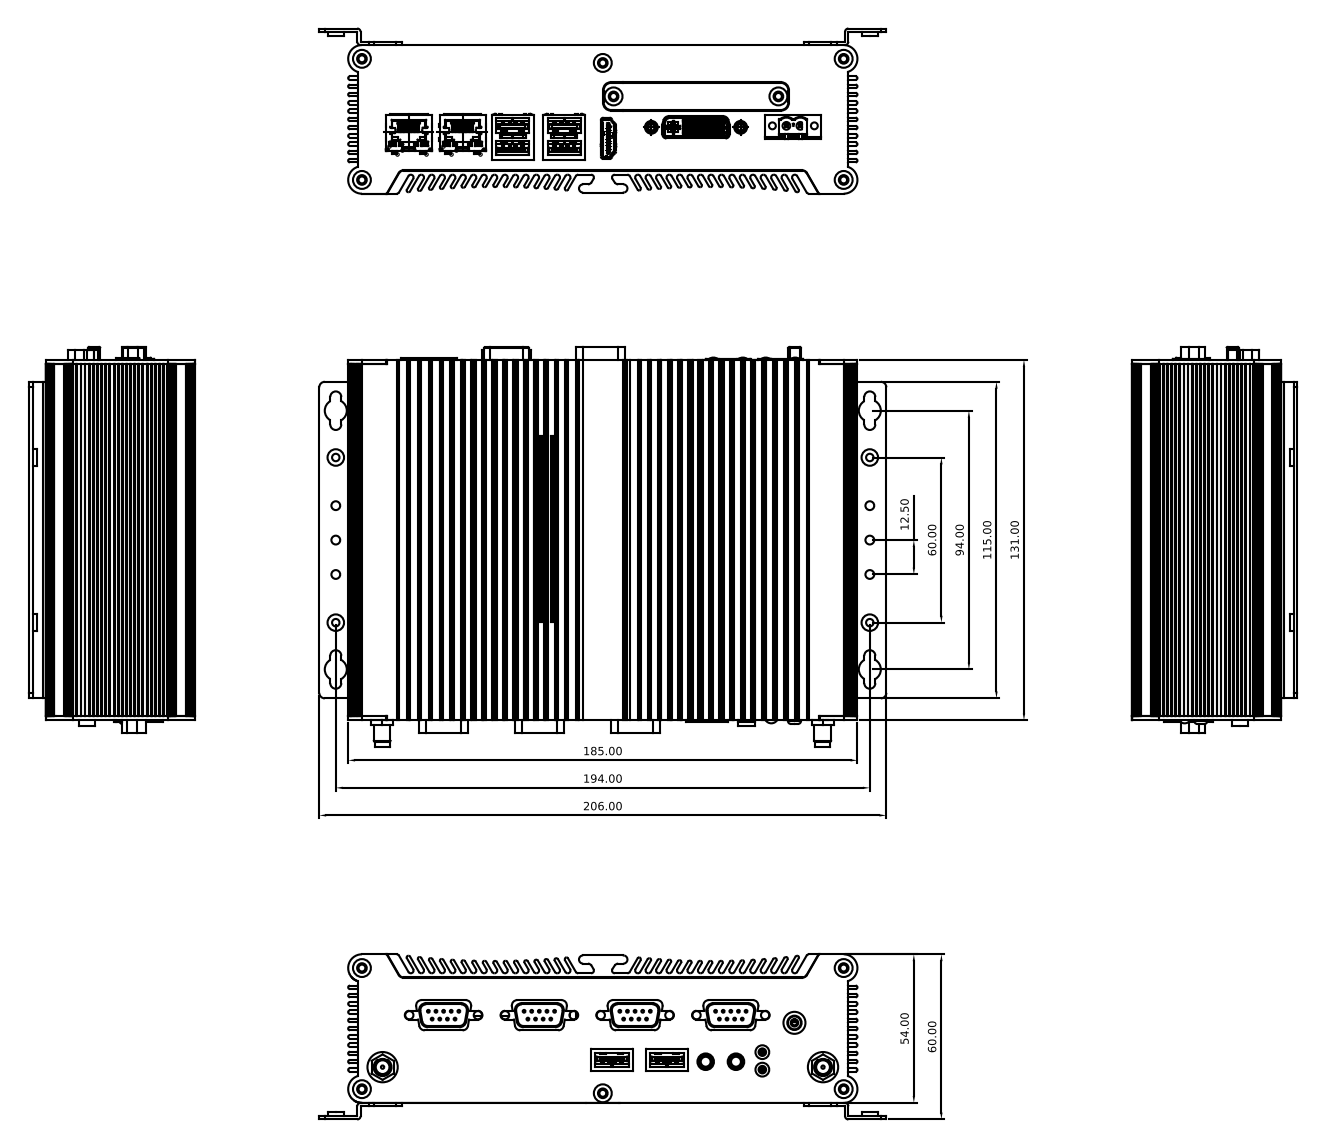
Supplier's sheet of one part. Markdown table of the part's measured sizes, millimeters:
| quantity | value |
| --- | --- |
| part name | NISE104 |
| STEP written by | SolidWorks 2011 (CONFIG_CONTROL_DESIGN) |
| units | millimeters |
| bodies | 0 solids, 2274 faces (1081 planar, 1081 cylindrical, 112 other) |
| overall size | 206 × 145 × 60 |
| round holes (diameter × count) | 3.05 × 10, 3.2 × 6, 3.5 × 6, 2.71 × 4, 5 × 4, 1.2 × 2, 2.5 × 2, 3.6 × 2, 7.5 × 2, 1.6 × 1, 5.5 × 1 |
| round bosses / shafts (diameter × count) | 1 × 36, 3 × 10, 6 × 6, 6.8 × 4, 6.7 × 4, 5.5 × 3, 7 × 2, 4.5 × 1 |
| partial cylindrical surfaces (radius × count) | 0.15 × 222, 1 × 137, 0.3 × 51, 2 × 44, 0.8 × 34, 0.6 × 30, 0.62 × 22, 0.5 × 18 |
| main face-to-face distances | 43.6, 18, 25.6, 3.29, 6.58, 9.87, 13.16, 129.5, 1.5, 32.91 |
| hole center spacings | 34.78, 194, 12.5, 17.5, 19, 24.9, 25.83, 30 |
